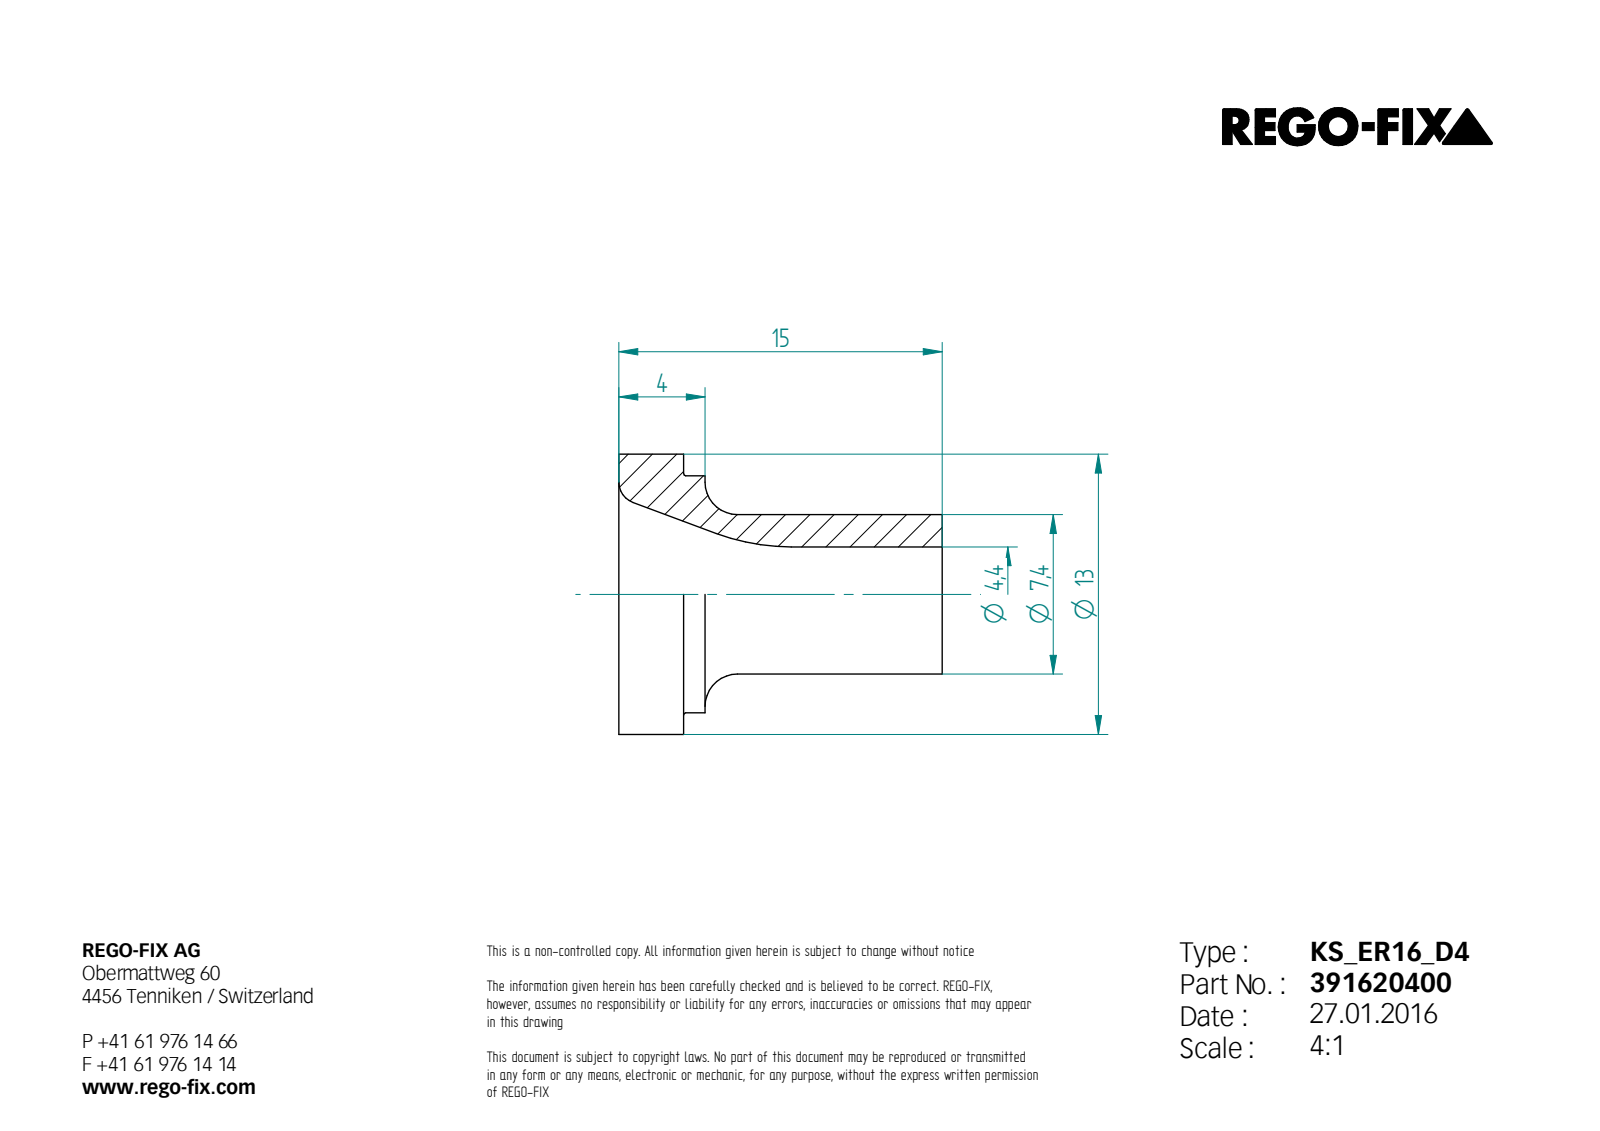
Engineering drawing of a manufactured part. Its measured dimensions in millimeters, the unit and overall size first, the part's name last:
Units: millimetres
Overall size (bounding box): 15 × 13 × 13
Round holes (diameter × count): ⌀4.4 ×1
Round bosses / shafts (diameter × count): ⌀13 ×1, ⌀11 ×1, ⌀7.4 ×1
Main face-to-face distances: 3, 15, 12, 4, 1, 11
Volume: 612 mm³ · Surface area: 841 mm²
Bodies: 1 solid, 13 faces (4 planar, 4 cylindrical, 5 other)
STEP written by: Unknown (AUTOMOTIVE_DESIGN)
